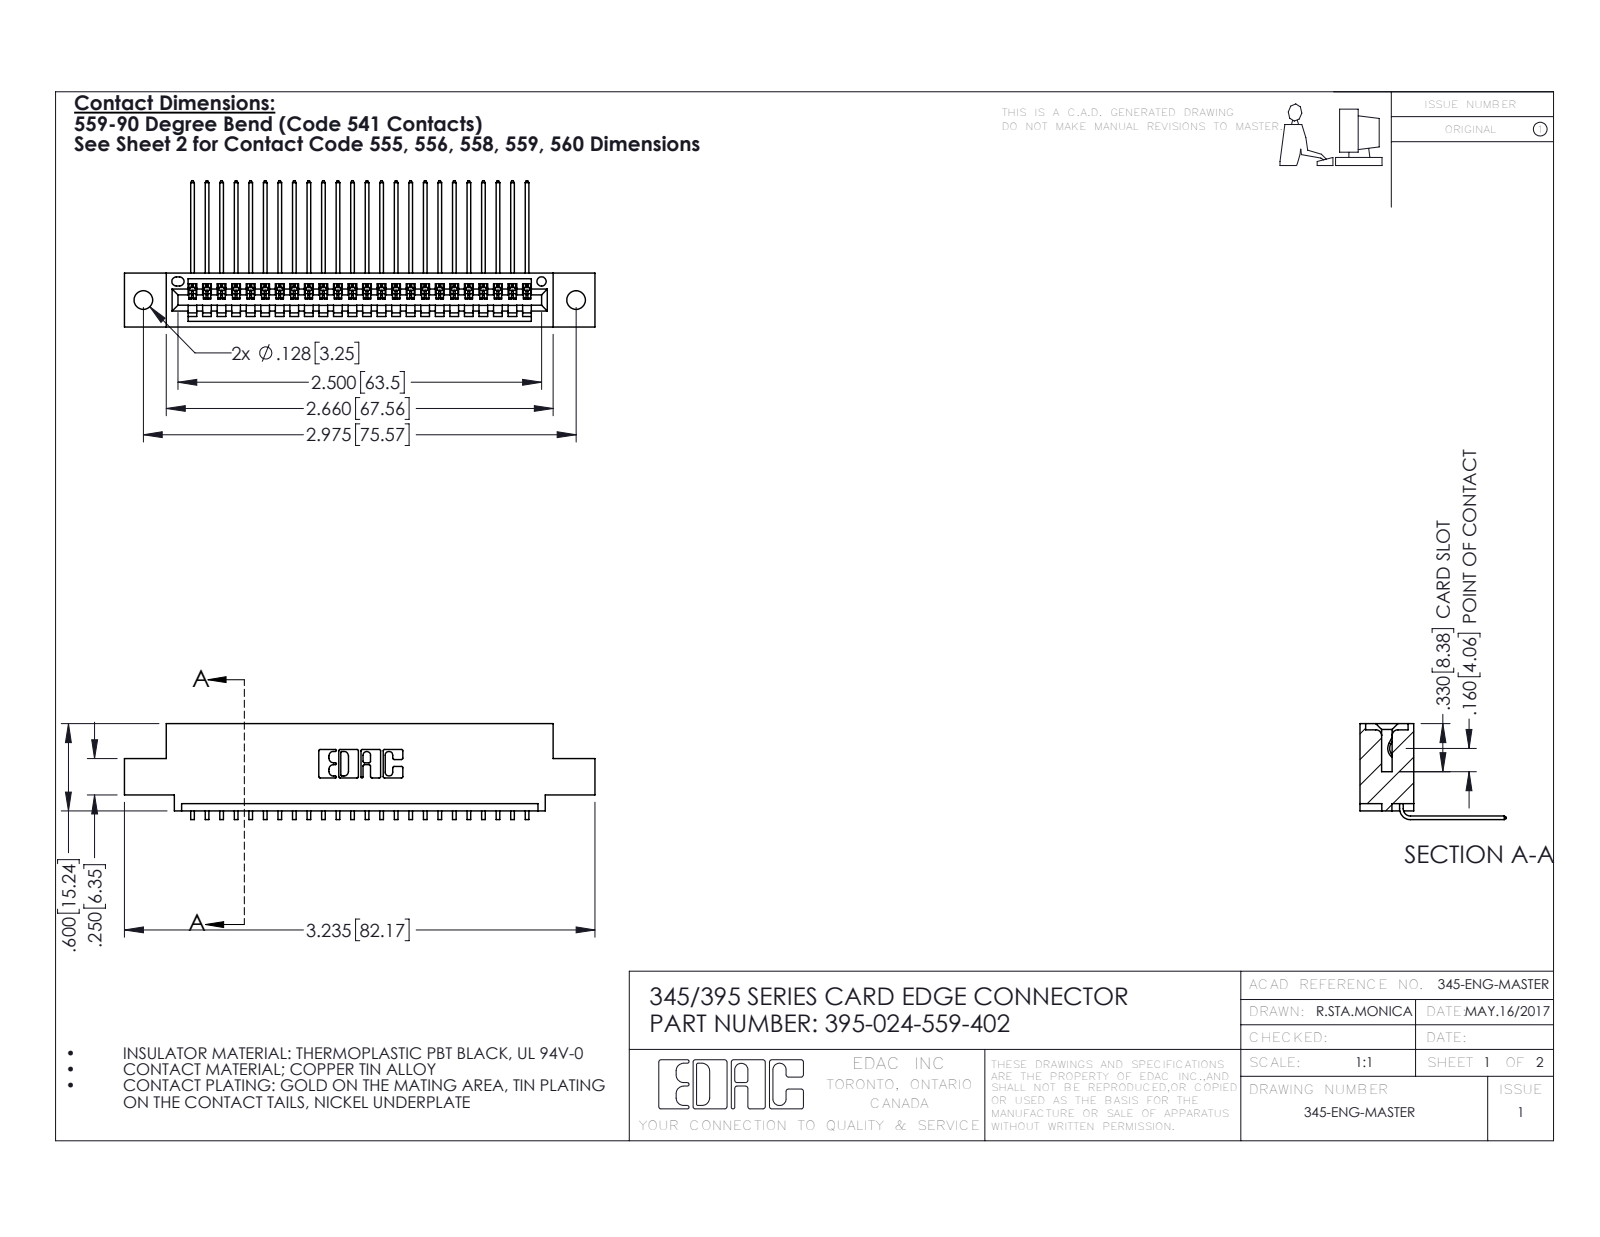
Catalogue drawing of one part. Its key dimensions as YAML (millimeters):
part_name: "395-024-559-402; 345-292-001_558 559 Tail - 1; 345 Part_0.110 Offset - 0.128 Dia"
step_written_by: "SolidWorks 2016 (CONFIG_CONTROL_DESIGN)"
units: millimeters
bodies: {solids: 25, faces: 1570, planar: 1092, cylindrical: 478, other: 0}
overall_size: [82.2, 25.5, 16.7]
volume: 7620
surface_area: 10170
round_holes:
  - {diameter: 3.3, count: 2}
  - {diameter: 1.6, count: 1}
partial_cylinders:
  - {radius: 0.2, count: 48}
  - {radius: 0.3, count: 22}
  - {radius: 0.2, count: 6}
  - {radius: 0.8, count: 6}
  - {radius: 0.7, count: 3}
  - {radius: 0.8, count: 2}
  - {radius: 1, count: 2}
  - {radius: 0.4, count: 1}
face_to_face_distances: [1.8, 7.6, 9.4, 5.1, 2.5, 6.9, 0.6, 5.7, 3.8, 1.8]
hole_center_spacings: [6.9, 69.6, 75.6]
